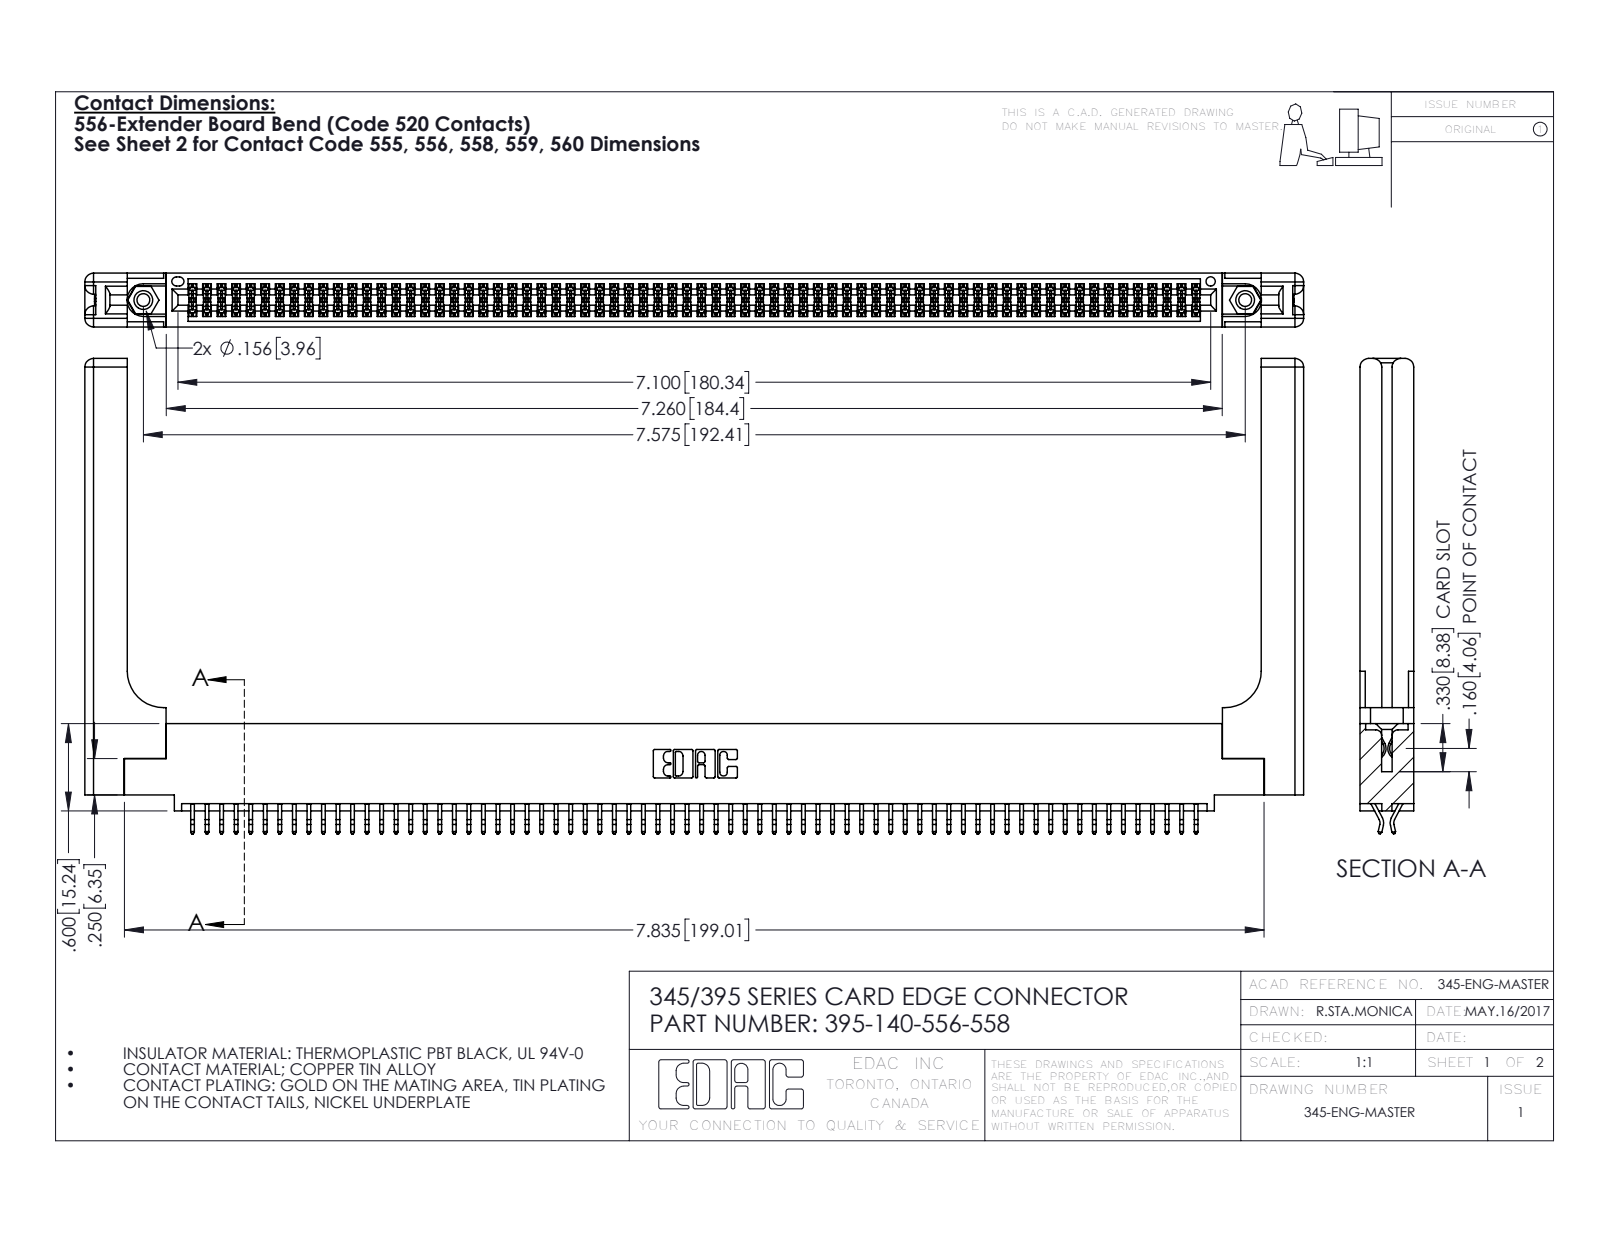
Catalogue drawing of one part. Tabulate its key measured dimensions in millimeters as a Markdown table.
| quantity | value |
| --- | --- |
| part name | 395-140-556-558; 345-250-001_345-250-001-102; 345-220-058_345-220-058; 345-292-001_556 Tail (+1 more) |
| STEP written by | SolidWorks 2016 (CONFIG_CONTROL_DESIGN) |
| units | millimeters |
| bodies | 145 solids, 8226 faces (5412 planar, 2754 cylindrical, 60 other) |
| overall size | 212.8 × 83 × 9.4 |
| volume | 29 330 mm³ |
| surface area | 36 400 mm² |
| round holes (diameter × count) | 2.3 × 2, 3.2 × 2, 4 × 2, 1.6 × 1 |
| round bosses / shafts (diameter × count) | 3.9 × 2 |
| partial cylindrical surfaces (radius × count) | 0.2 × 210, 0.3 × 22, 1.5 × 16, 0.2 × 6, 0.8 × 6, 0.7 × 3, 0.3 × 2, 0.4 × 2 |
| main face-to-face distances | 1.8, 7.6, 9.4, 0.6, 2.5, 6.9, 5.1, 5.7, 3.8, 3.8 |
| hole center spacings | 6.9, 186.4, 192.4 |
